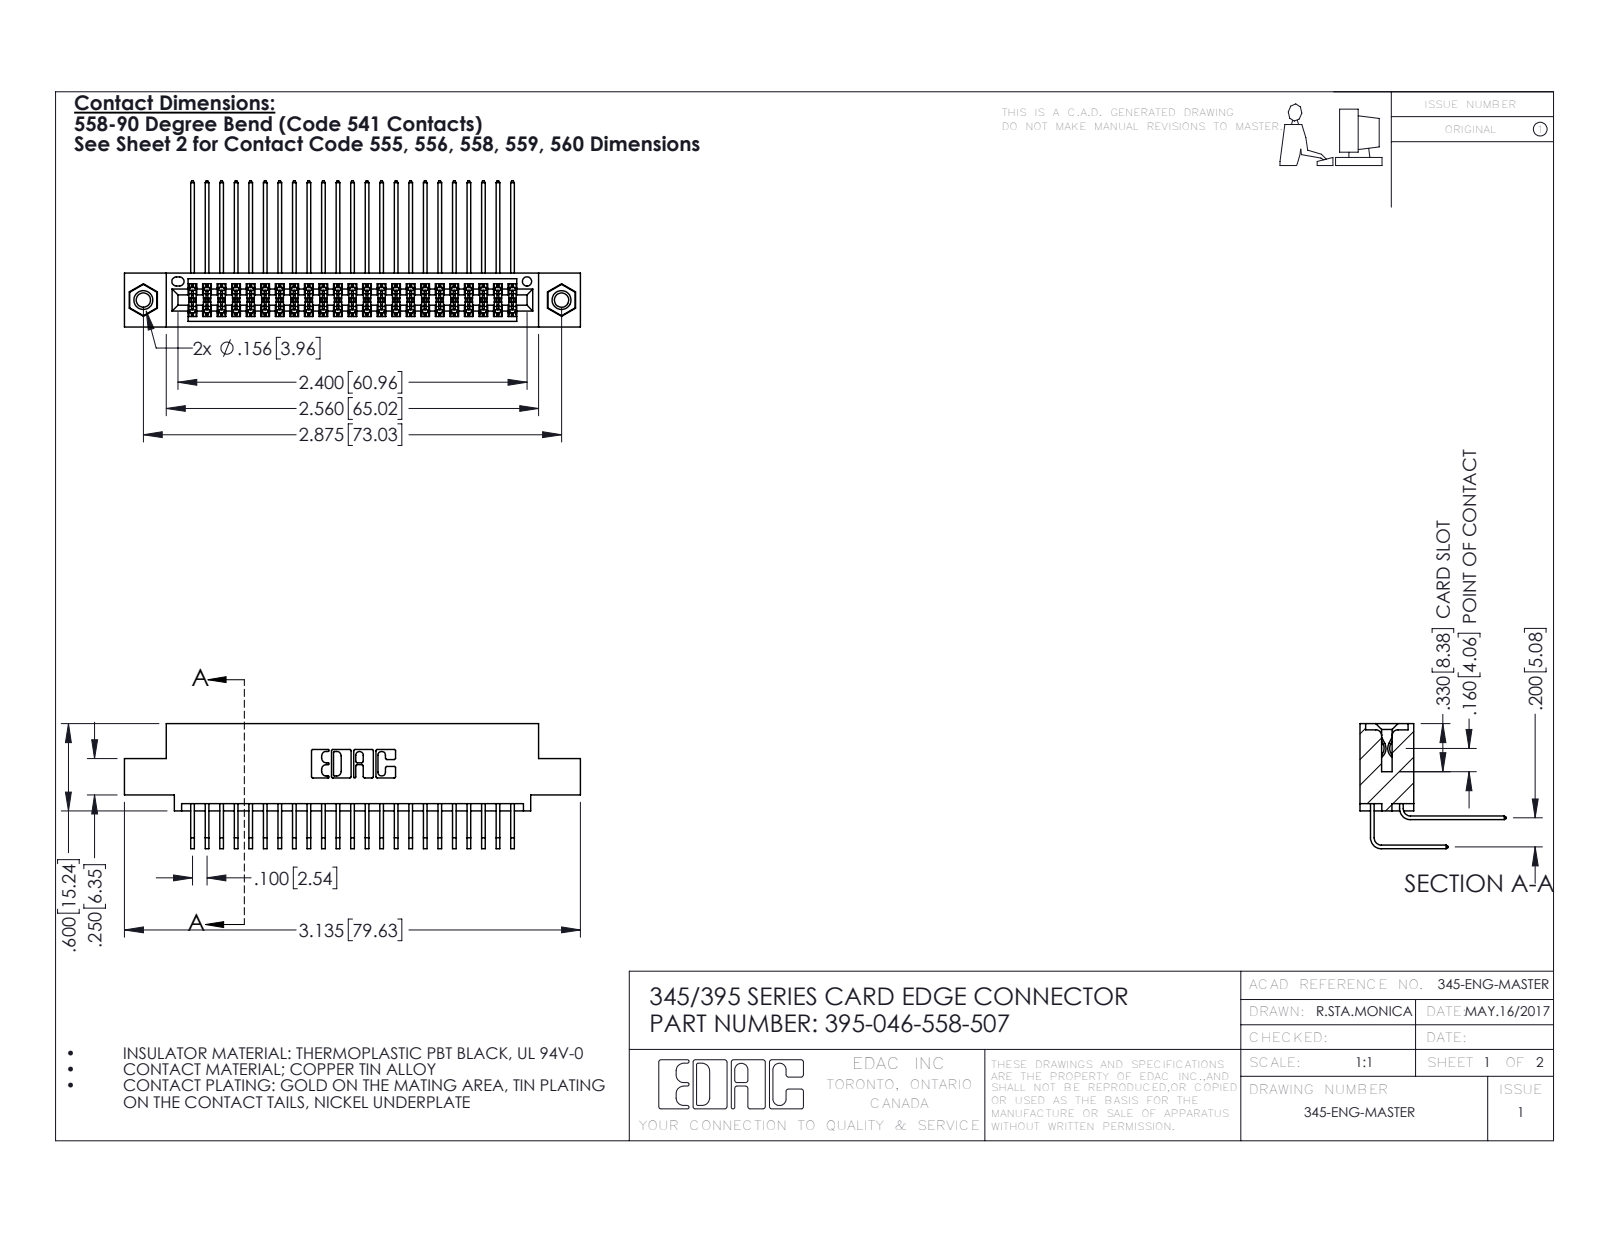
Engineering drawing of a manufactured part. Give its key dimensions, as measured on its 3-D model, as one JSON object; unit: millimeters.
{"part_name": "395-046-558-507; 345-292-001_558 559 Tail - 1; 345-292-001_558 Tail - 2; 345 Part_0.110 Offset - 0.156 Dia-TI (+1 more)", "step_written_by": "SolidWorks 2016 (CONFIG_CONTROL_DESIGN)", "units": "millimeters", "bodies": {"solids": 49, "faces": 2582, "planar": 1726, "cylindrical": 840, "other": 16}, "overall_size": [79.6, 25.5, 21.8], "volume_mm3": 7730, "surface_area_mm2": 12440, "round_holes": [[2.5, 2], [3.2, 2], [4, 2], [1.6, 1]], "round_bosses_or_shafts": [[3.9, 2]], "partial_cylinders_radius": [[0.2, 70], [0.3, 22], [0.2, 6], [0.8, 6], [0.7, 3], [0.4, 2], [0.5, 2], [0.6, 2]], "face_to_face_distances": [5.1, 1.8, 7.6, 9.4, 2.5, 6.9, 0.6, 5.7, 0.6, 4.4], "hole_center_spacings": [6.9, 67.1, 73]}
